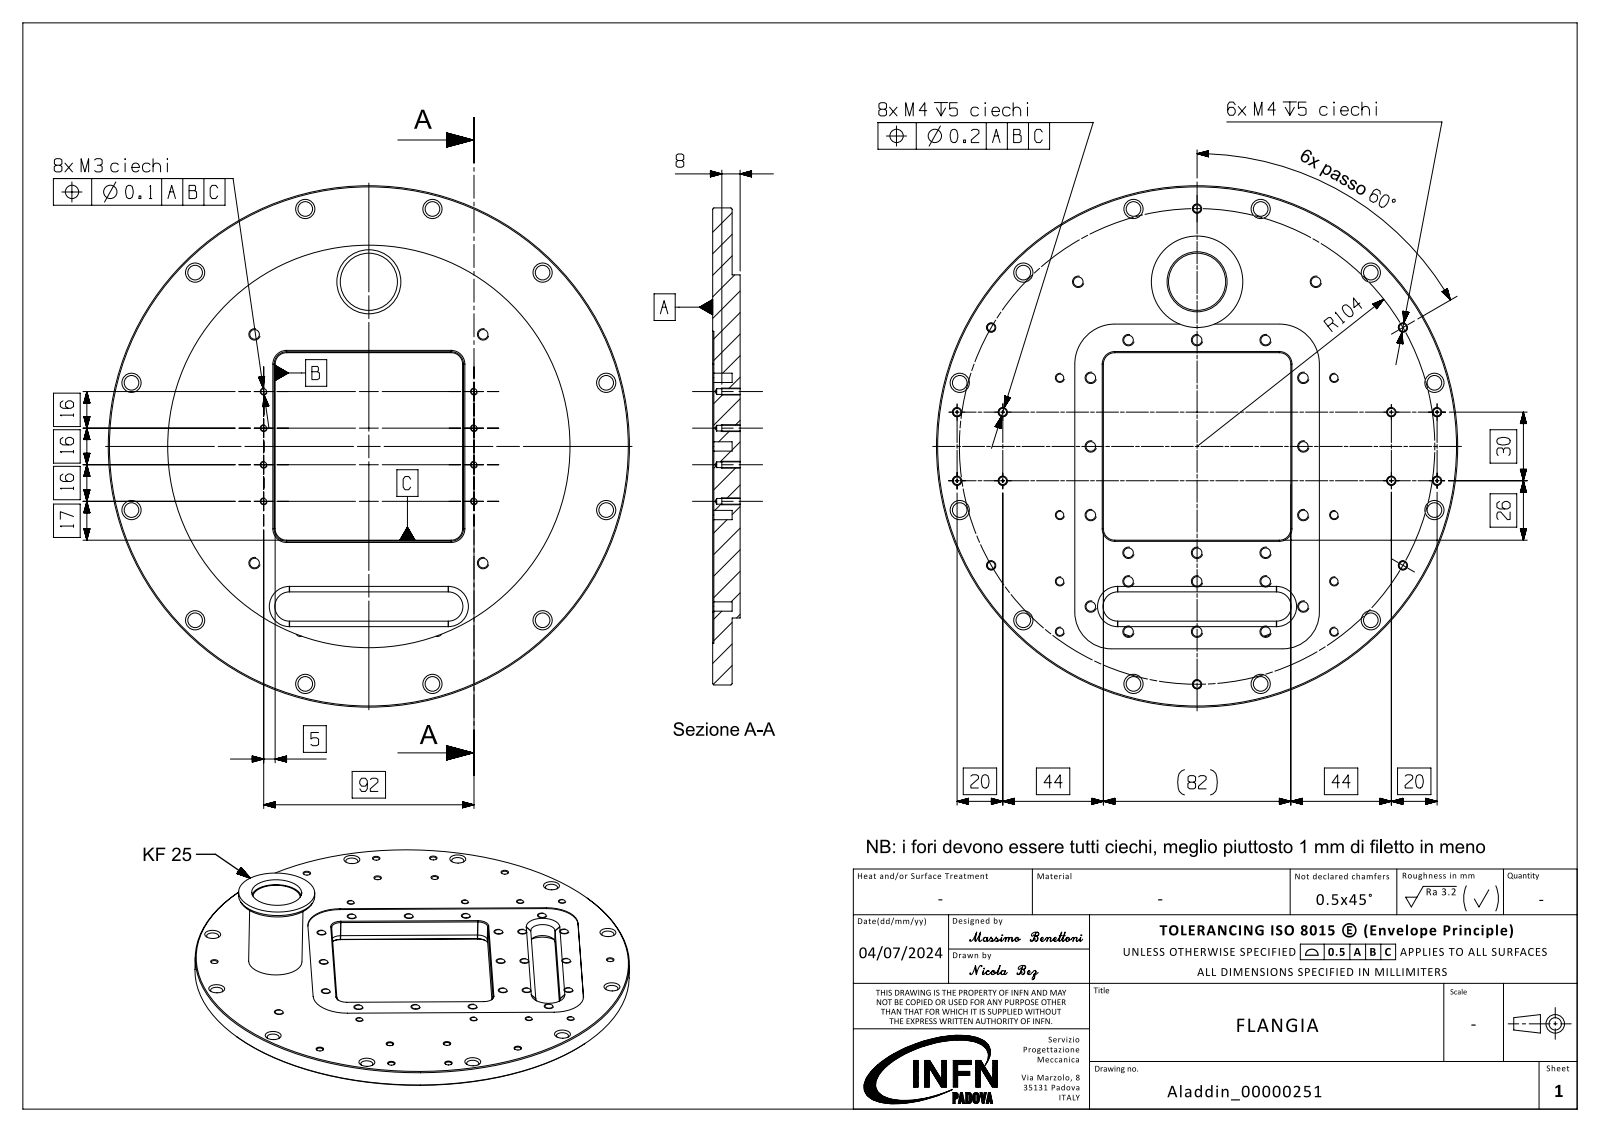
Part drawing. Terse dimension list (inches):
name: IR3_00000251_objects
written by: SIEMENS PLM Software NX2306.9102 (AUTOMOTIVE_DESIGN)
unit: in
bodies: 2 solids, 232 faces (57 planar, 85 cylindrical, 90 other)
size: 8.976 × 8.976 × 2.126
volume: 20 in³; area: 146.5 in²
holes: 26× ⌀0.165, 22× ⌀0.13, 12× ⌀0.252, 8× ⌀0.098, 1× ⌀0.984, 1× ⌀1.033, 1× ⌀1.102
bosses: 1× ⌀8.976, 1× ⌀6.929, 1× ⌀1.575
rounds: 4× R0.197, 2× R0.252, 2× R0.63, 2× R0.689
face distances: 0.335, 0.138, 0.472, 0.02, 0.315, 0.453, 3.228, 2.126, 1.988, 1.673
hole spacings: 1.181, 1.943, 3.081, 3.524, 3.847, 3.661, 2.362, 3.937
